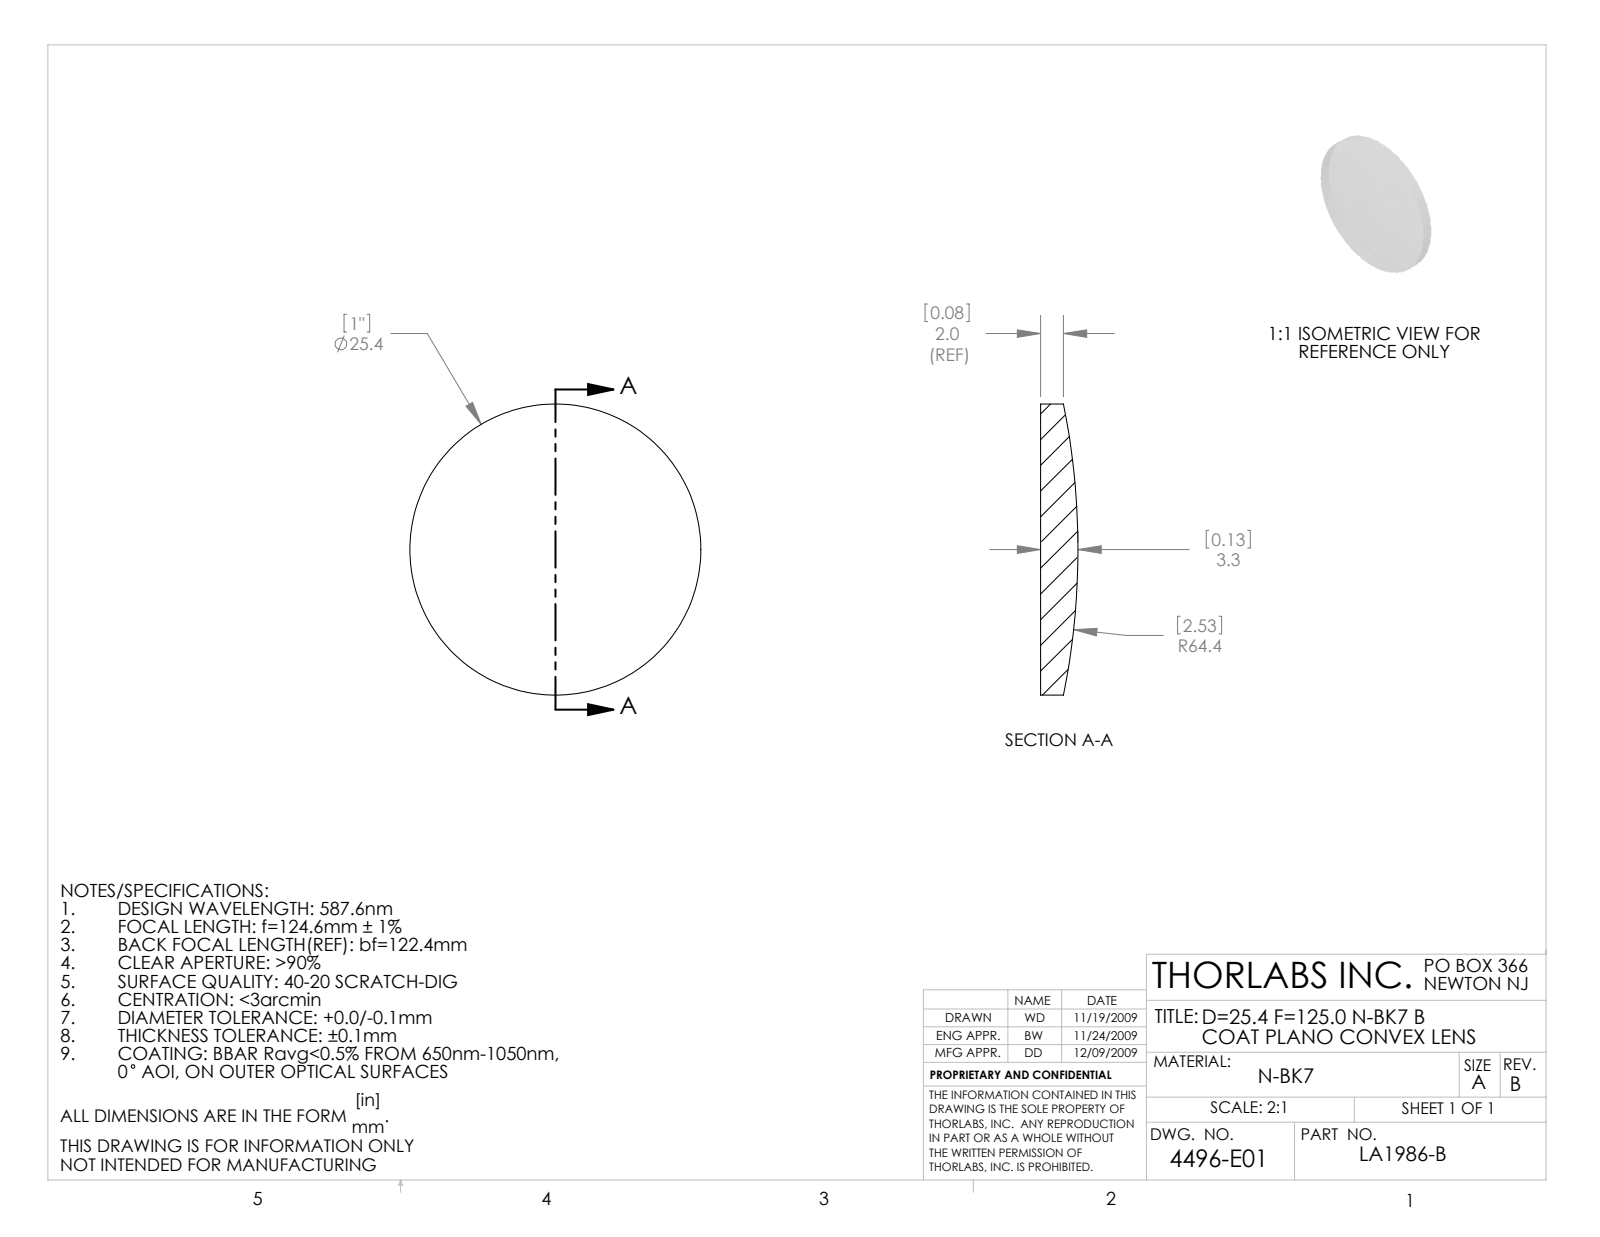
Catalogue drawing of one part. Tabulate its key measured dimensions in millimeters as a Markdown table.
| quantity | value |
| --- | --- |
| part name | 4496-E0W |
| STEP written by | SolidWorks 2009 (AUTOMOTIVE_DESIGN) |
| units | millimeters |
| bodies | 1 solid, 5 faces (1 planar, 2 cylindrical, 2 other) |
| overall size | 25.4 × 25.4 × 3.26 |
| volume | 1 332 mm³ |
| surface area | 1 178 mm² |
| round bosses / shafts (diameter × count) | 25.4 × 1 |
